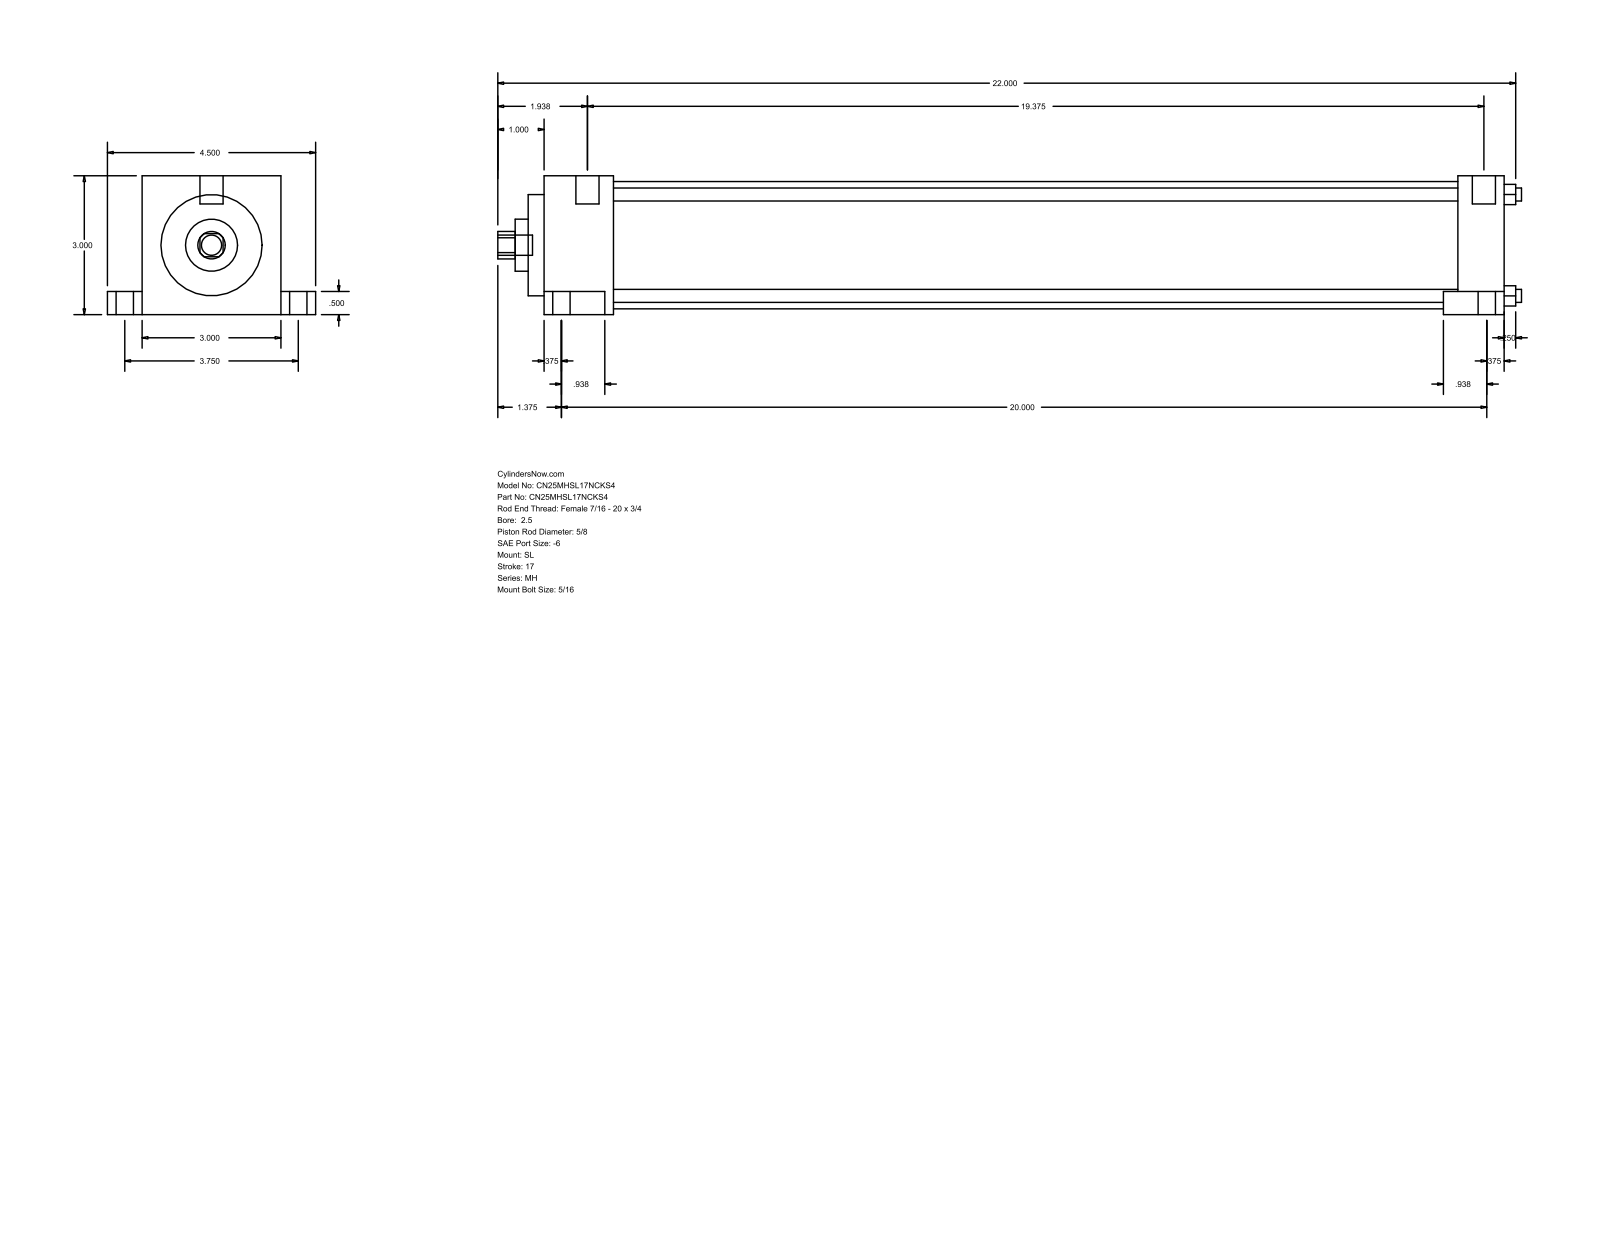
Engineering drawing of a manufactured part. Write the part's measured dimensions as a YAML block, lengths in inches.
part_name: "MH_SL__0250_0.625"
step_written_by: "GSSL Pune (CONFIG_CONTROL_DESIGN)"
units: inches
bodies: {solids: 0, faces: 86, planar: 61, cylindrical: 25, other: 0}
overall_size: [22.125, 4.5, 3]
round_holes:
  - {diameter: 0.281, count: 4}
  - {diameter: 0.625, count: 1}
  - {diameter: 1.125, count: 1}
  - {diameter: 2.187, count: 1}
  - {diameter: 2.75, count: 1}
round_bosses_or_shafts:
  - {diameter: 0.625, count: 2}
  - {diameter: 0.375, count: 2}
  - {diameter: 0.219, count: 2}
  - {diameter: 0.5, count: 1}
  - {diameter: 0.437, count: 1}
partial_cylinders:
  - {radius: 0.297, count: 1}
face_to_face_distances: [3, 1, 20.094, 21.094, 0.5, 2.5, 0.75, 3.75, 1.25, 19.781]
hole_center_spacings: [1.548, 2.19, 3.097]
